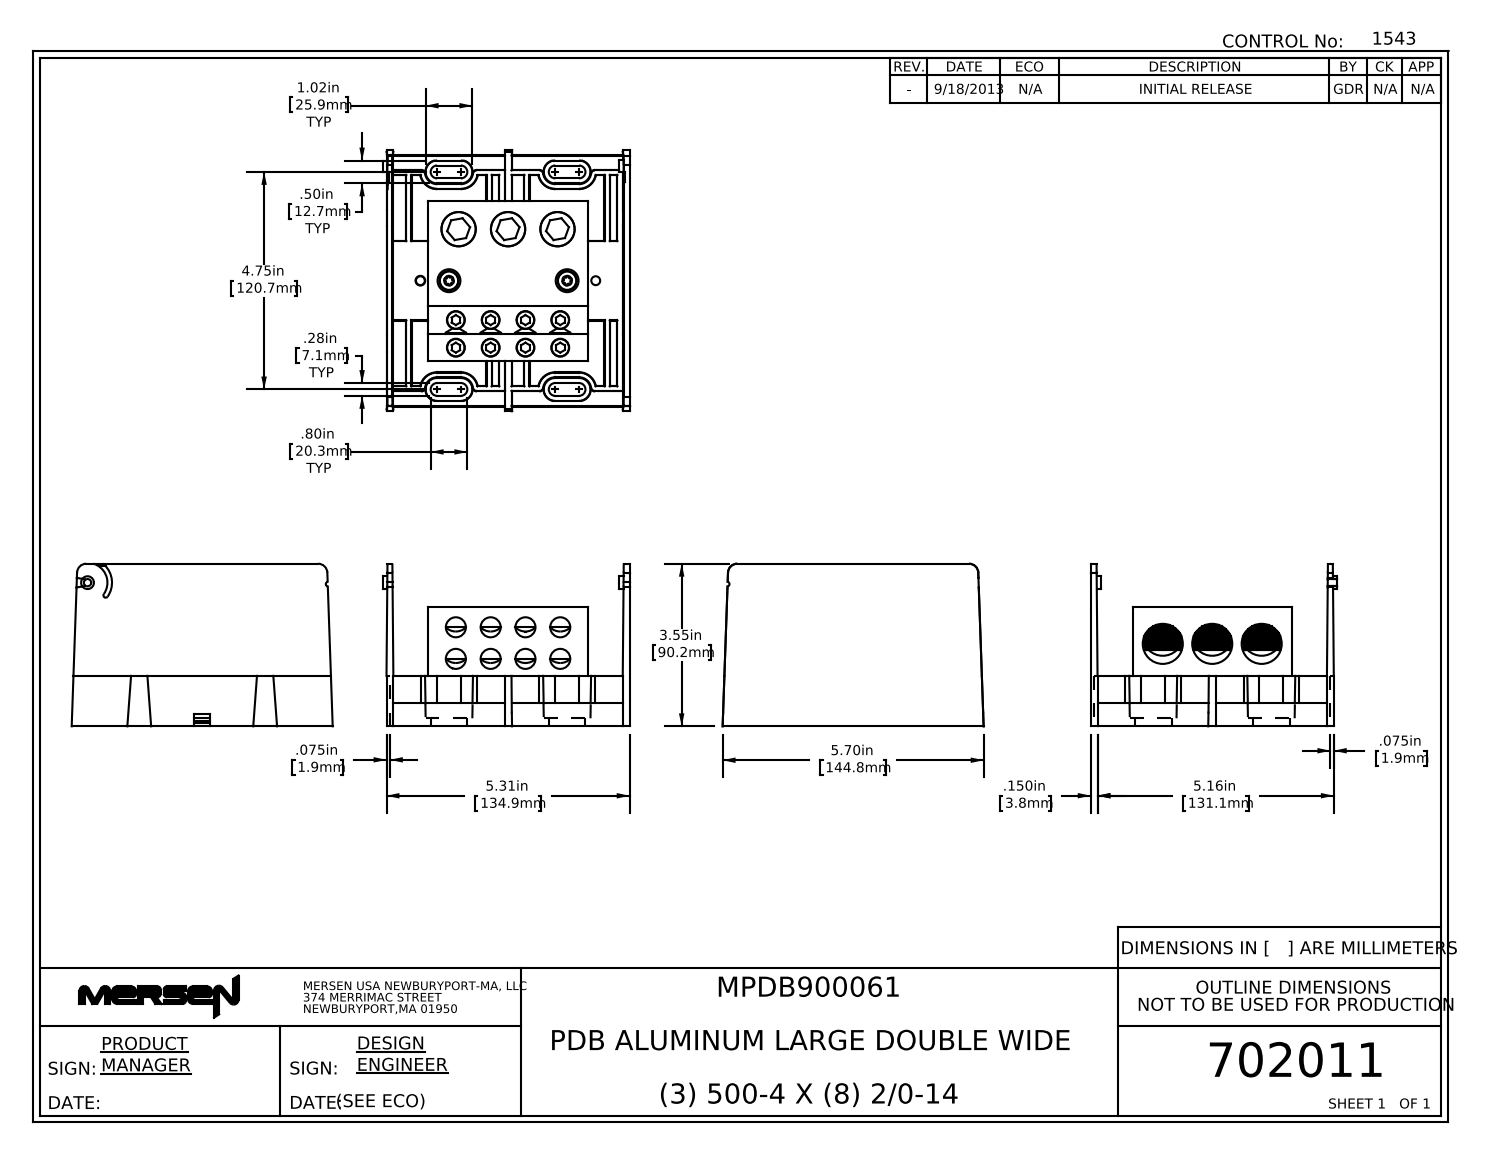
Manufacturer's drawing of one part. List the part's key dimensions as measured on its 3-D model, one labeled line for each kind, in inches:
Part name (STEP PRODUCT): 420243
STEP written by: SolidWorks 2013 (AUTOMOTIVE_DESIGN)
Units: inches
Bodies: 17 solids, 1067 faces (643 planar, 170 cylindrical, 254 other)
Overall size (bounding box): 5.7 × 5.385 × 3.55
Volume: 28.94 in³ · Surface area: 357.5 in²
Round holes (diameter × count): ⌀0.391 ×8, ⌀0.437 ×8, ⌀0.194 ×4, ⌀0.75 ×3, ⌀0.875 ×3, ⌀0.272 ×2, ⌀0.5 ×2, ⌀0.16 ×1
Round bosses / shafts (diameter × count): ⌀0.438 ×8, ⌀0.425 ×2, ⌀0.28 ×2, ⌀0.216 ×2, ⌀0.157 ×2
Partial cylindrical surfaces — rounded edges, fillets, slot ends (radius × count): R0.035 ×28, R0.01 ×20, R0.019 ×12, R0.031 ×12, R0.1 ×10, R0.141 ×8, R0.2 ×2, R0.435 ×2
Main face-to-face distances: 2.58, 5.16, 0.125, 0.4, 0.525, 0.15, 2.45, 0.85, 0.575, 0.915
Hole centre spacings: 0.76, 1.52, 1.026, 0.603, 0.69, 0.76, 0.97, 1.635
